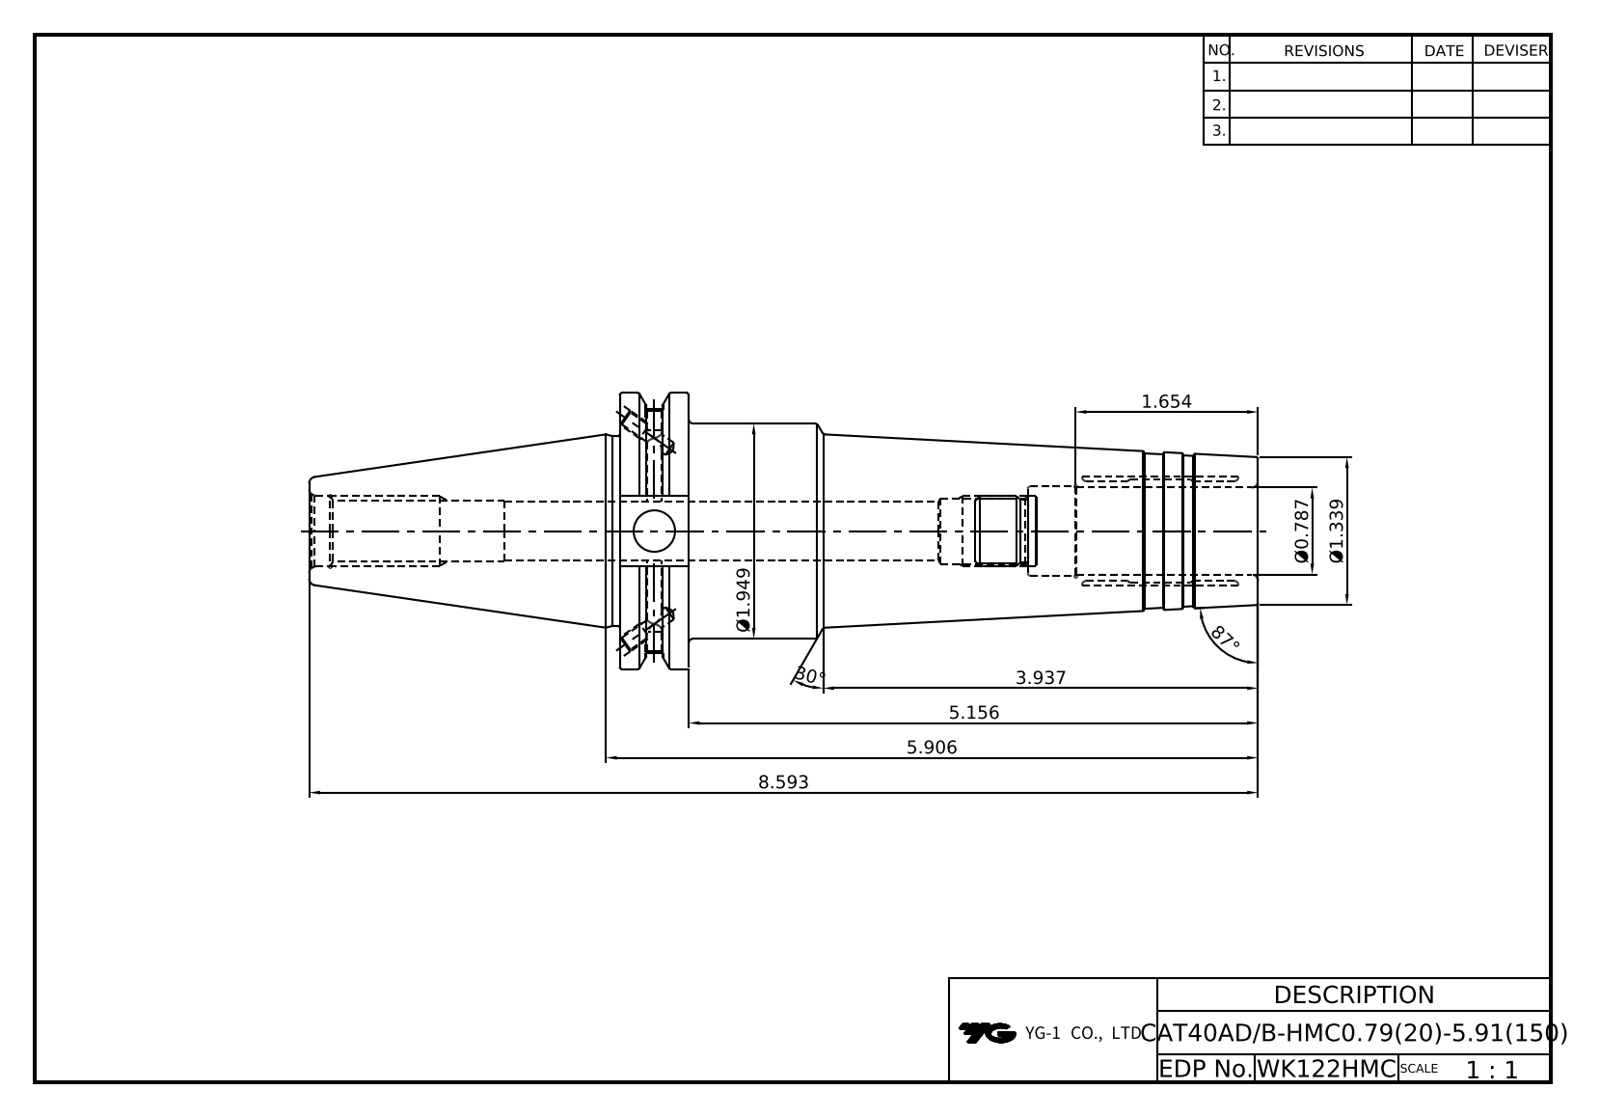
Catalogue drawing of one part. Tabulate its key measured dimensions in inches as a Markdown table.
| quantity | value |
| --- | --- |
| part name | LO-CAT40ADB-HMC20-150 |
| STEP written by | Autodesk Inventor 2020 (AUTOMOTIVE_DESIGN) |
| units | inches |
| bodies | 1 solid, 106 faces (36 planar, 30 cylindrical, 40 other) |
| overall size | 8.593 × 2.5 × 2.405 |
| volume | 15.45 in³ |
| surface area | 67.7 in² |
| round holes (diameter × count) | 0.128 × 4, 0.157 × 2, 0.165 × 2, 0.375 × 1, 0.512 × 1, 0.527 × 1, 0.587 × 1, 0.642 × 1, 0.787 × 1, 0.803 × 1 |
| round bosses / shafts (diameter × count) | 2.5 × 1, 1.949 × 1, 1.717 × 1 |
| partial cylindrical surfaces (radius × count) | 0.322 × 1, 1.108 × 1 |
| main face-to-face distances | 0.625, 5.781, 5.156, 1.874, 0.645, 3.694, 3.069, 2.087, 2.812, 3.437 |
